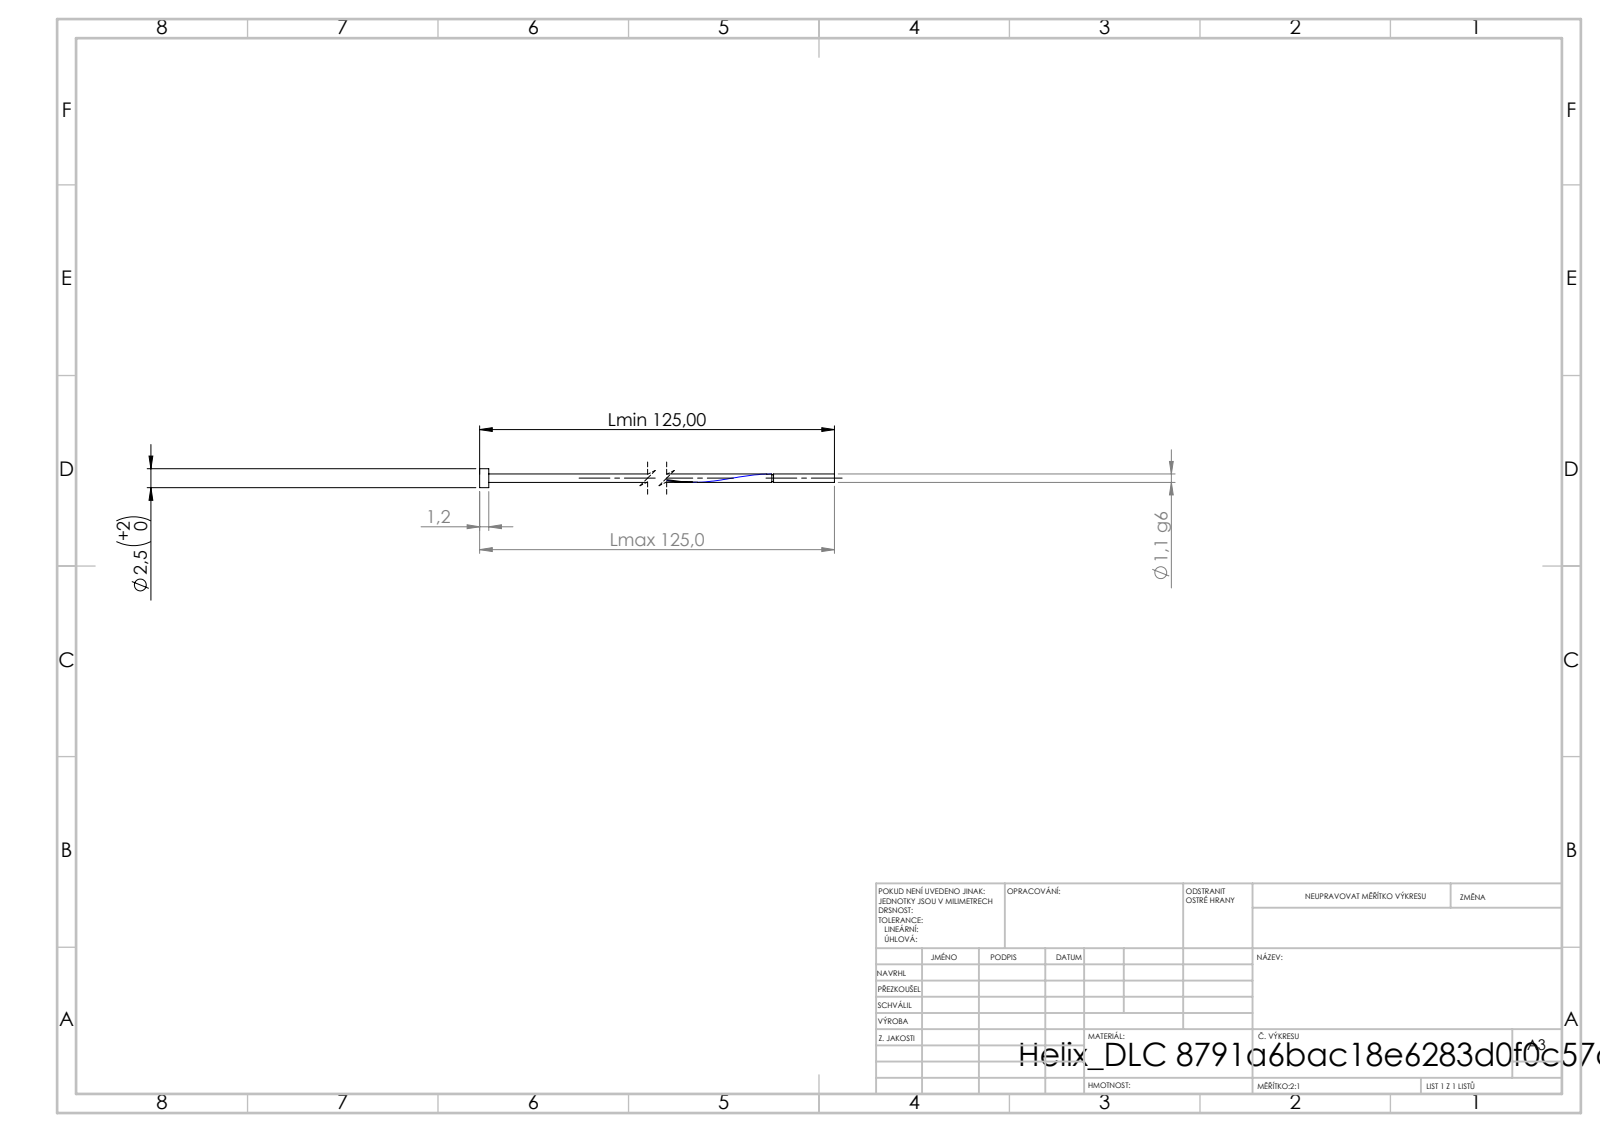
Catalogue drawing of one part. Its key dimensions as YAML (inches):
step_written_by: "SolidWorks 2019 (CONFIG_CONTROL_DESIGN)"
units: inches
bodies: {solids: 1, faces: 16, planar: 6, cylindrical: 9, other: 1}
overall_size: [4.921, 0.098, 0.098]
volume: 0.009
surface_area: 0.927
round_bosses_or_shafts:
  - {diameter: 0.098, count: 1}
  - {diameter: 0.043, count: 1}
  - {diameter: 0.035, count: 1}
face_to_face_distances: [0.047, 4.921, 4.874, 4.607, 4.559, 0.315, 4.598, 4.551, 0.323, 2.137]
